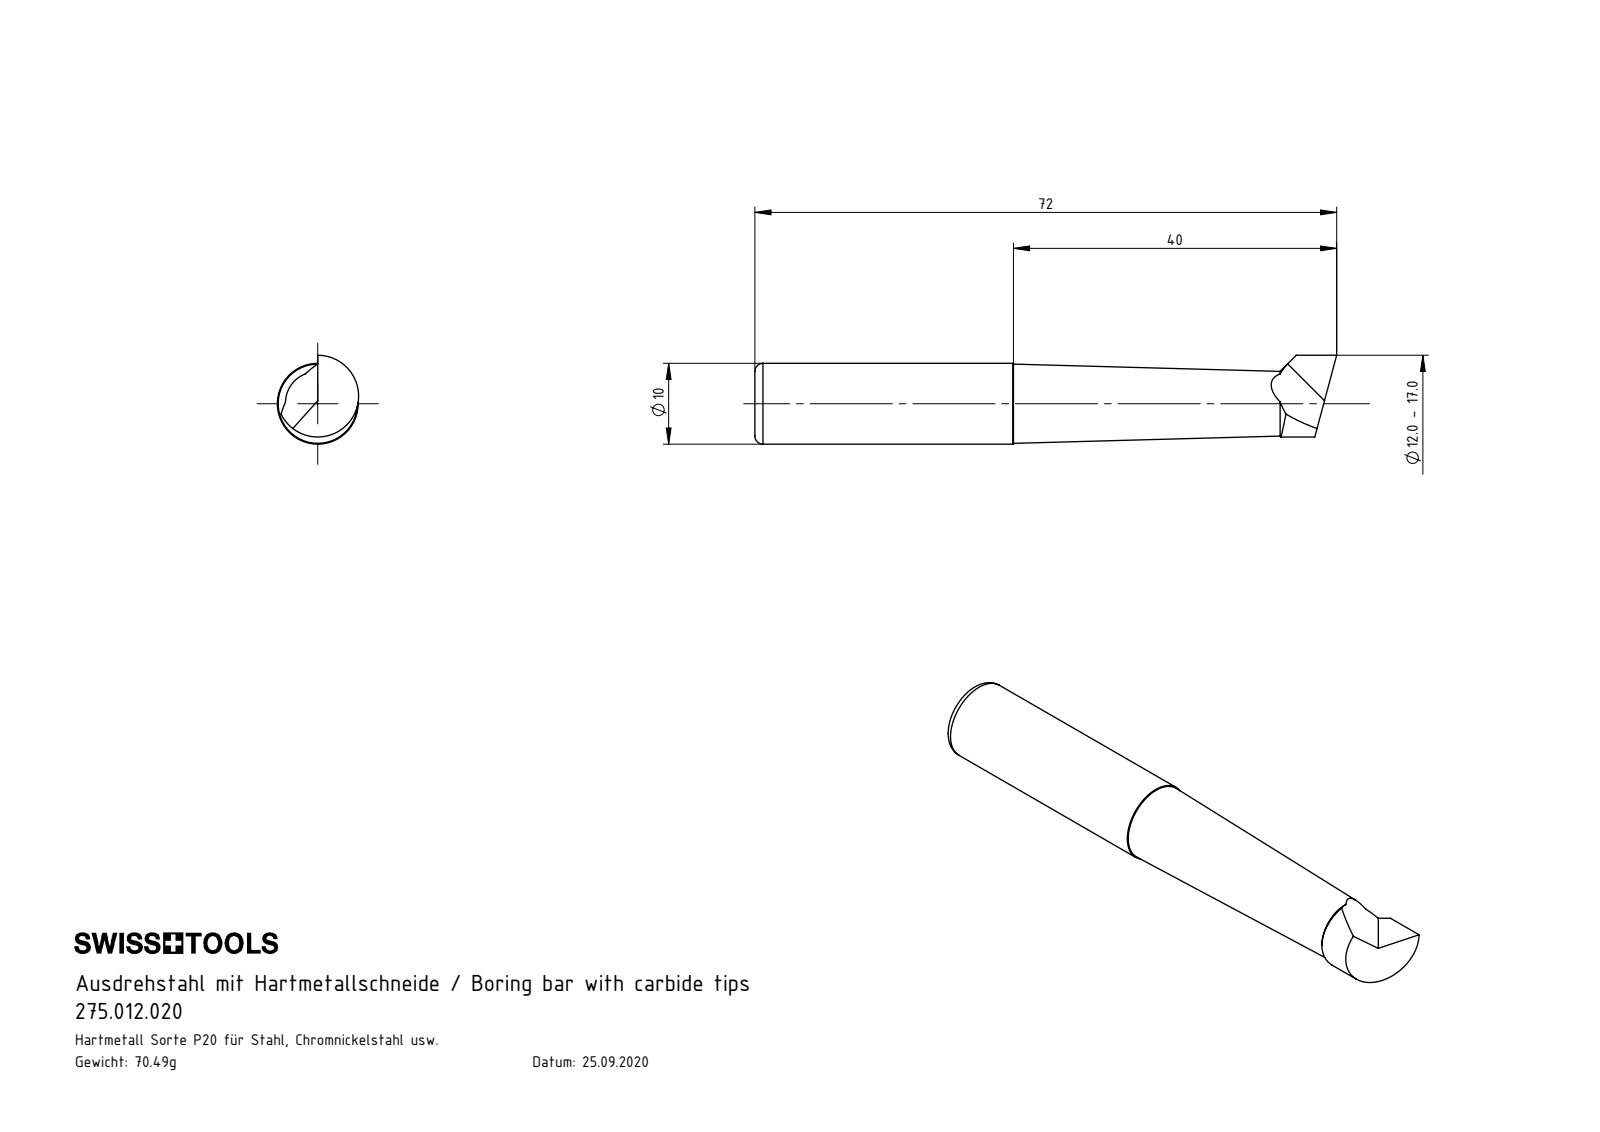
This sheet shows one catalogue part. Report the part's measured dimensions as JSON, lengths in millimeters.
{"part_name": "275.012.020", "step_written_by": "SolidWorks 2022 (CONFIG_CONTROL_DESIGN)", "units": "millimeters", "bodies": {"solids": 1, "faces": 16, "planar": 4, "cylindrical": 3, "other": 9}, "overall_size": [72, 11, 10.06], "volume_mm3": 4862, "surface_area_mm2": 2217, "round_bosses_or_shafts": [[10, 1]], "partial_cylinders_radius": [[5.06, 1]]}
